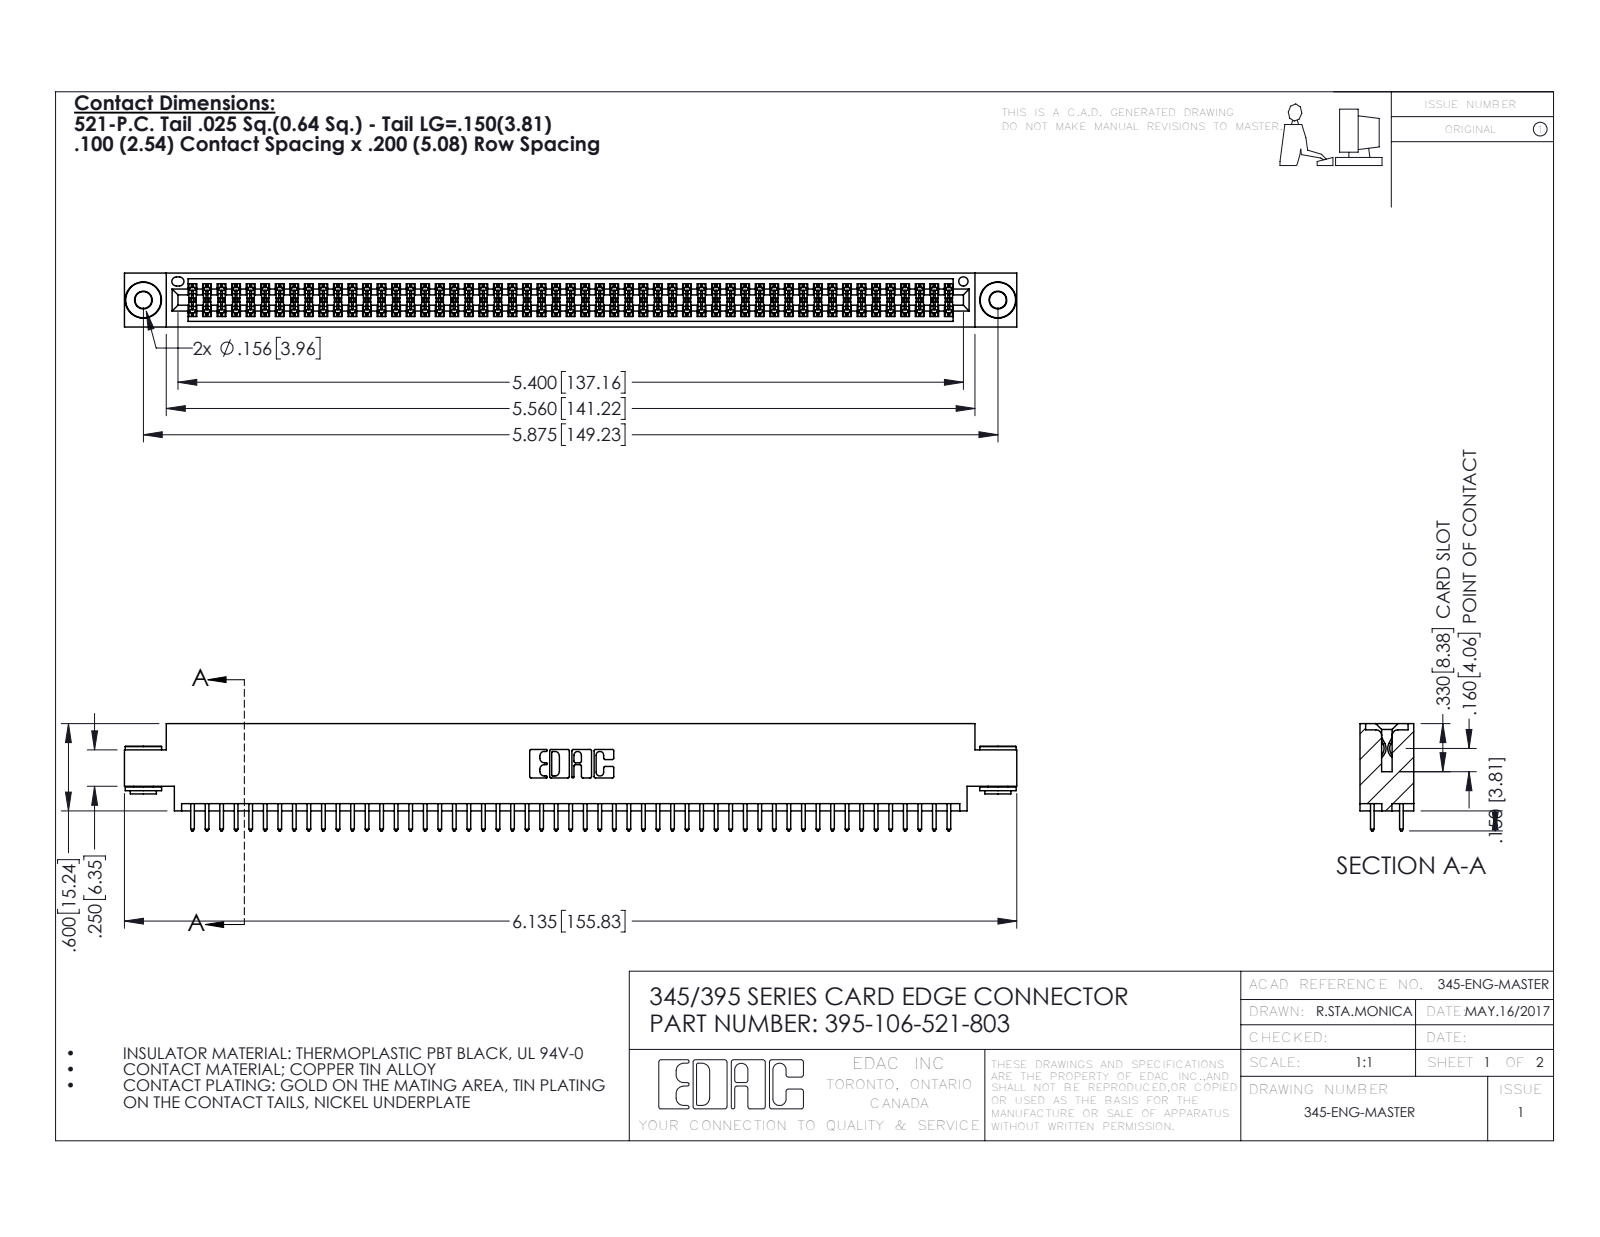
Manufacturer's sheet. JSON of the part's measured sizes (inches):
{"part_name": "395-106-521-803; 345-250-002_345-250-002-102; 345-292-001_345-293-121; 345 Part_0.170 Offset - 0.156 Dia-TH", "step_written_by": "SolidWorks 2016 (CONFIG_CONTROL_DESIGN)", "units": "inches", "bodies": {"solids": 109, "faces": 5468, "planar": 3592, "cylindrical": 1868, "other": 8}, "overall_size": [6.135, 0.737, 0.37], "volume_in3": 0.922, "surface_area_in2": 35.04, "round_holes": [[0.116, 2], [0.156, 2], [0.064, 1]], "round_bosses_or_shafts": [[0.25, 2], [0.18, 2], [0.136, 2]], "partial_cylinders_radius": [[0.006, 159], [0.01, 106], [0.01, 22], [0.007, 6], [0.031, 6], [0.026, 3], [0.014, 2], [0.019, 2]], "face_to_face_distances": [0.072, 0.298, 0.37, 0.2, 0.098, 0.272, 0.025, 0.225, 0.175, 0.149], "hole_center_spacings": [0.27, 5.639, 5.875]}
